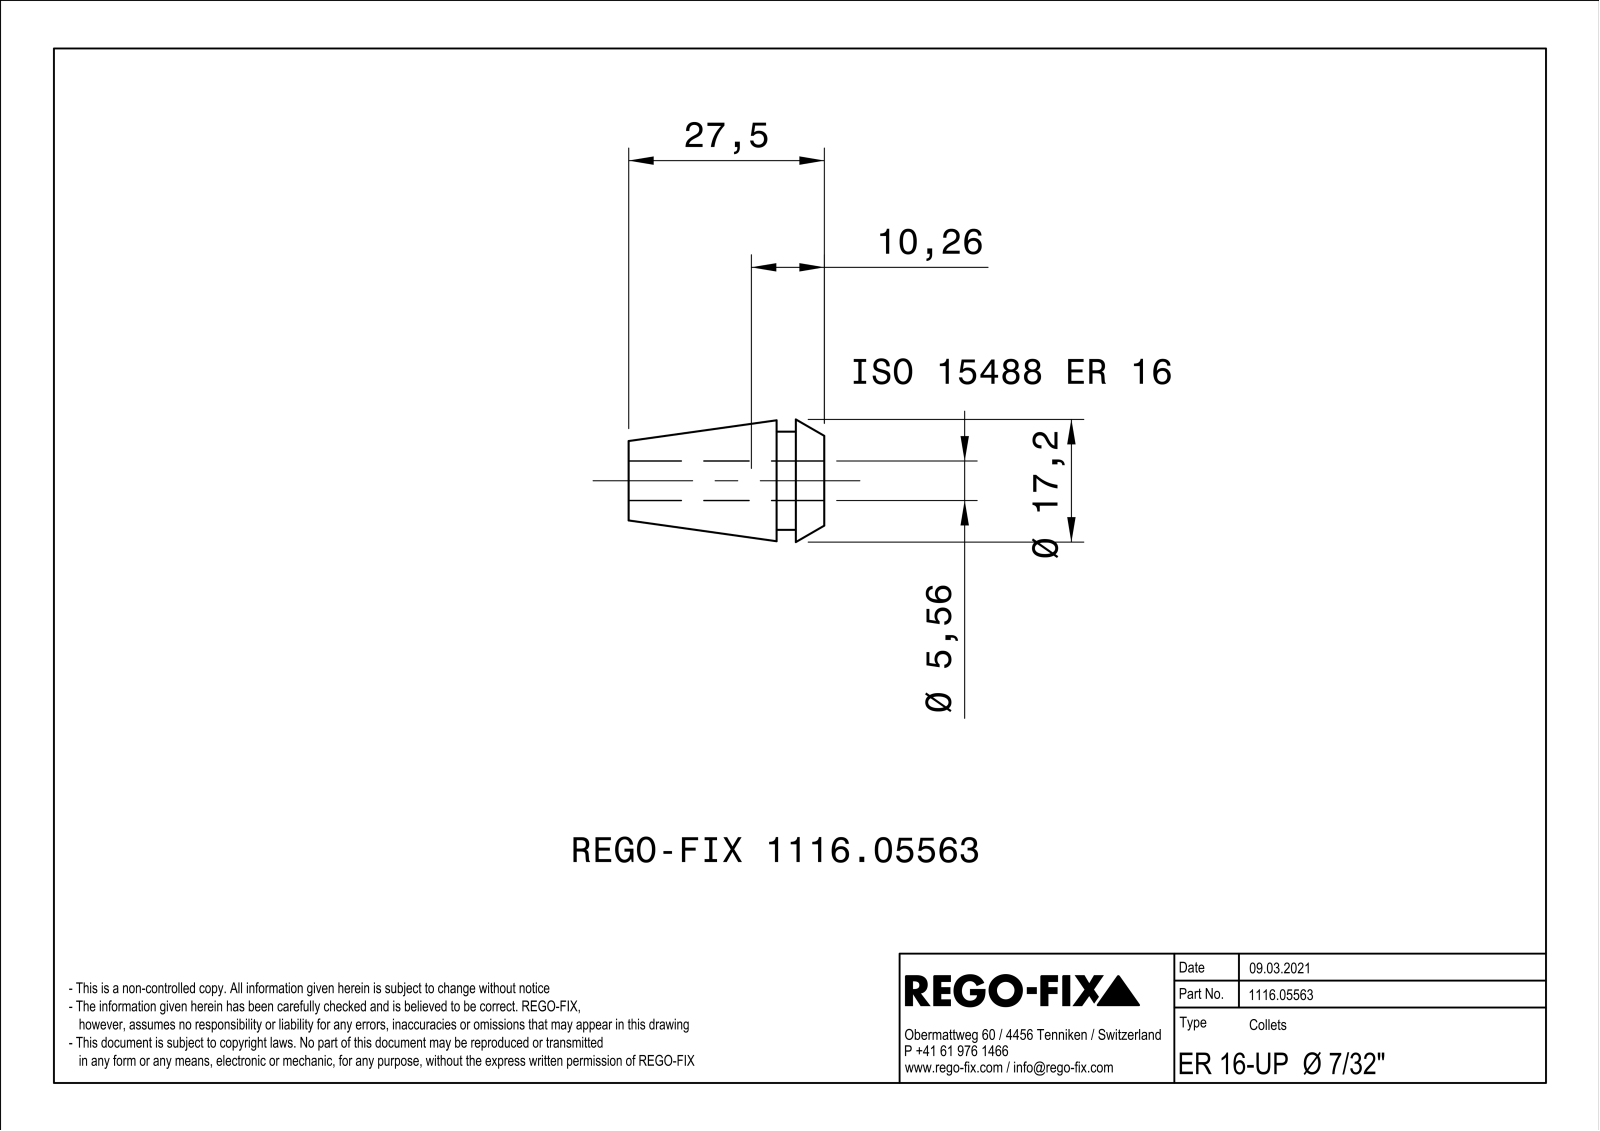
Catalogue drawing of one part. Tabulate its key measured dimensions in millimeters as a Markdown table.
| quantity | value |
| --- | --- |
| part name | NOCUT |
| STEP written by | SIEMENS PLM Software Solid Edge ST10 (AUTOMOTIVE_DESIGN) |
| units | millimeters |
| bodies | 1 solid, 201 faces (88 planar, 41 cylindrical, 72 other) |
| overall size | 27.5 × 17.24 × 17.24 |
| volume | 2 924 mm³ |
| surface area | 4 894 mm² |
| round holes (diameter × count) | 5.56 × 1 |
| round bosses / shafts (diameter × count) | 13.8 × 1 |
| partial cylindrical surfaces (radius × count) | 30 × 16 |
| main face-to-face distances | 0.5, 0.48, 0.52, 4, 6.7, 2.7, 27.5, 23.5, 20.8, 4.5 |
